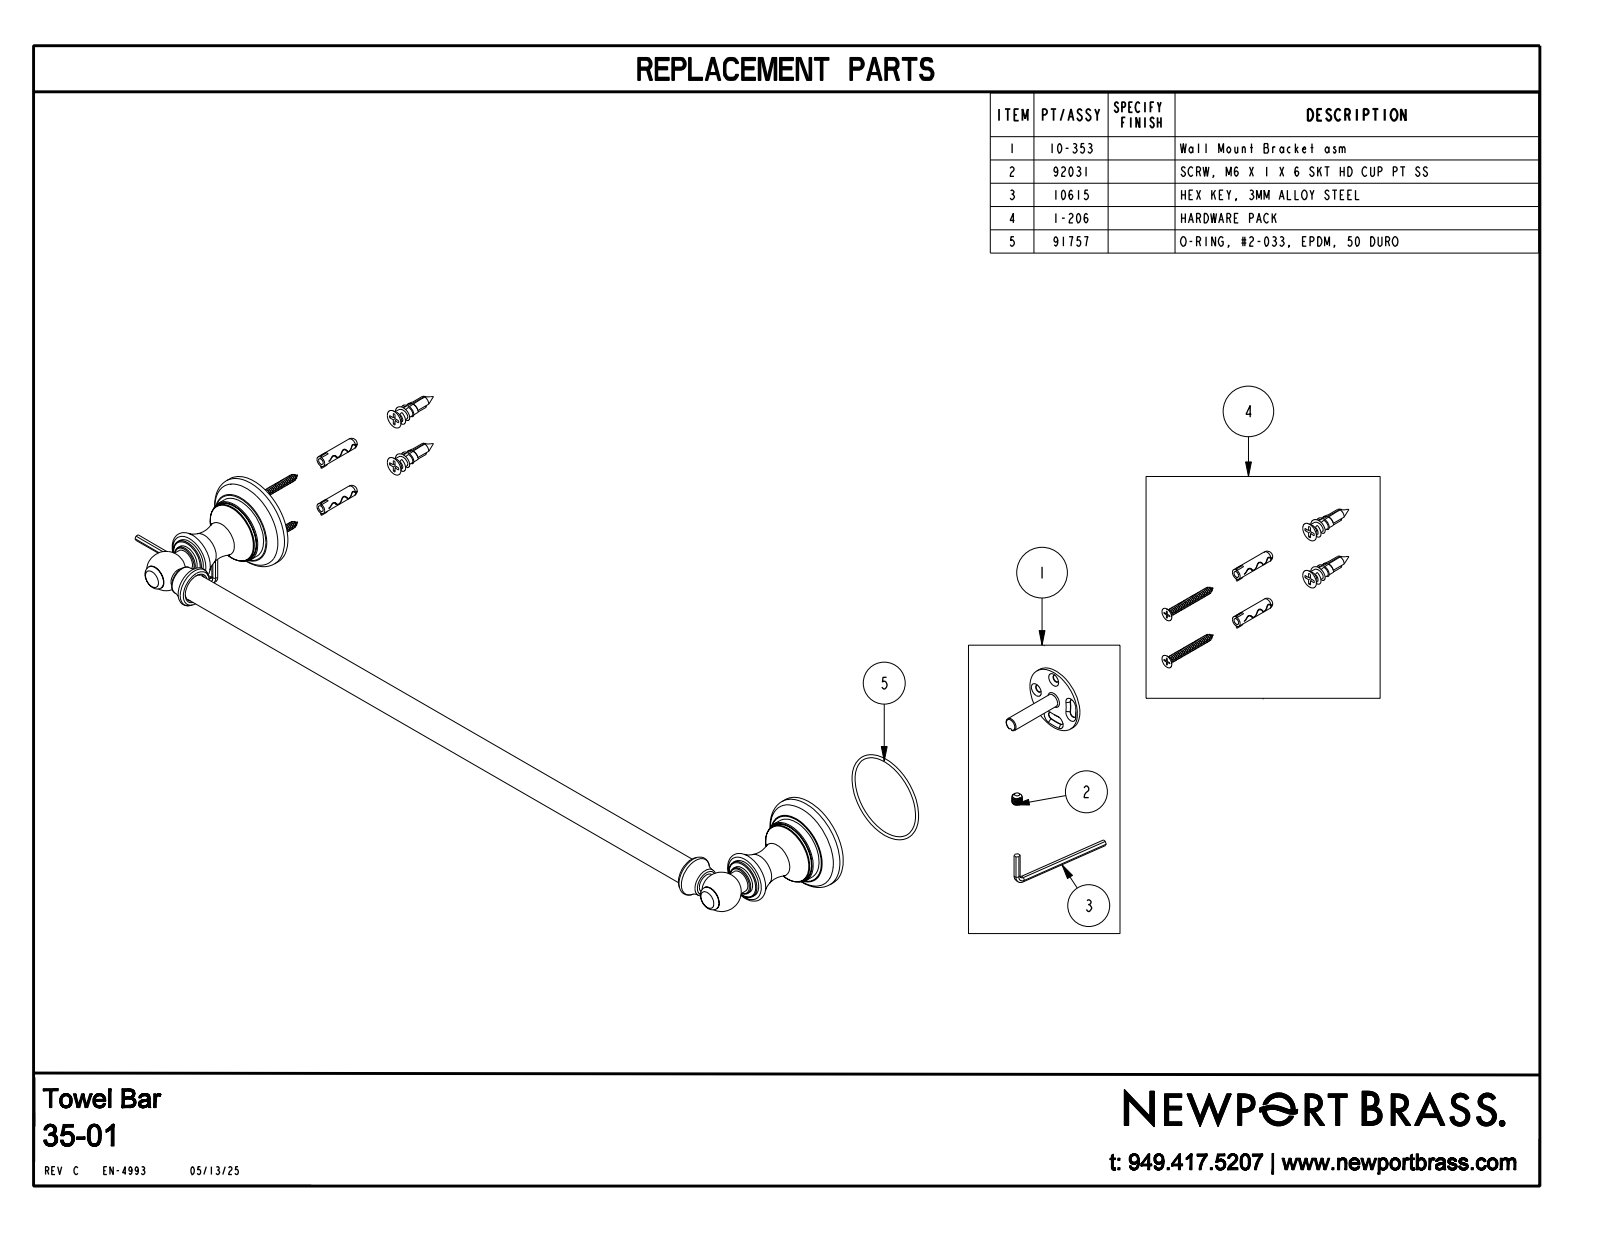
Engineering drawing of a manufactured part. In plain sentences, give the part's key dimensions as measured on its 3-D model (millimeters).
The part is named "11609; 2-656_ASM; 40720; 40734 (+3 more)". Its 3-D file was written by "CREO PARAMETRIC BY PTC INC, 2018400 (CONFIG_CONTROL_DESIGN)". It is 7 solids with 375 faces: 48 planar, 145 cylindrical and 182 other. Overall it measures 513.1 by 84.7 by 55.9 millimeters. Its volume is 88 310 cubic millimeters and its surface area 75 740 square millimeters. Round holes: 2 of diameter 5, 2 of diameter 6.4, 2 of diameter 8.2, 2 of diameter 31.8, 2 of diameter 34.8, 2 of diameter 48.5, 2 of diameter 53.9, 1 of diameter 4.9, 1 of diameter 7.1, 1 of diameter 14.4, 1 of diameter 16.6, 1 of diameter 19.2. Round bosses or shafts: 2 of diameter 55.9, 2 of diameter 49.9, 2 of diameter 37.8, 2 of diameter 36.1, 2 of diameter 34.3, 2 of diameter 22.9, 2 of diameter 16.8, 2 of diameter 14.2. The main face-to-face distances are 0.5, 9.5, 10, 1.4, 10.9, 11.4, 2, 1.3, 53.1, 51.7. The hole center spacings are 457.2.
